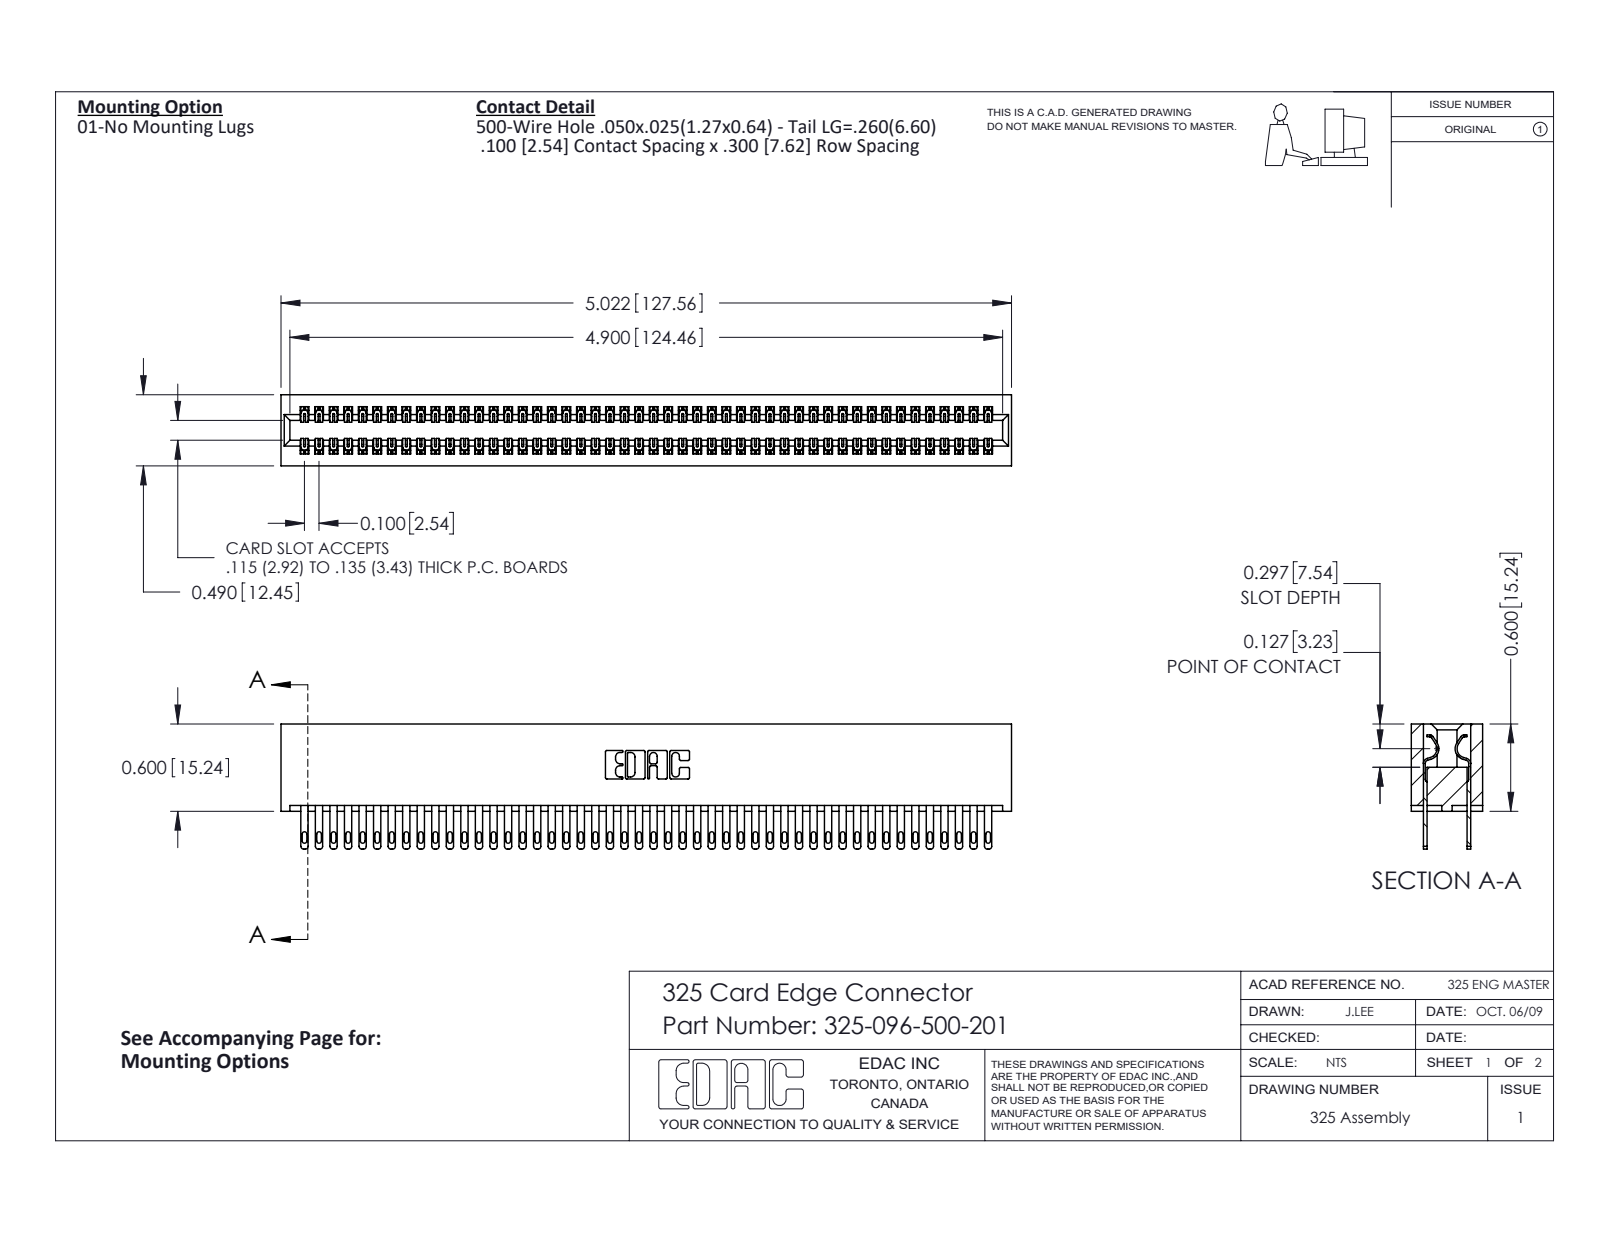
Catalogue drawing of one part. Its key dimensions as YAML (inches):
part_name: "325 Part_Lugless; 325-096-500-201; 325-292-001_325-293-100"
step_written_by: "SolidWorks 2016 (CONFIG_CONTROL_DESIGN)"
units: inches
bodies: {solids: 97, faces: 4714, planar: 2946, cylindrical: 1768, other: 0}
overall_size: [5.022, 0.86, 0.49]
volume: 1.063
surface_area: 35.48
partial_cylinders:
  - {radius: 0.006, count: 144}
  - {radius: 0.016, count: 96}
  - {radius: 0.02, count: 96}
  - {radius: 0.01, count: 22}
  - {radius: 0.007, count: 6}
  - {radius: 0.031, count: 6}
  - {radius: 0.026, count: 3}
  - {radius: 0.014, count: 2}
face_to_face_distances: [0.083, 0.407, 0.3, 0.107, 0.383, 0.025, 0.325, 0.49, 0.275, 0.56]
